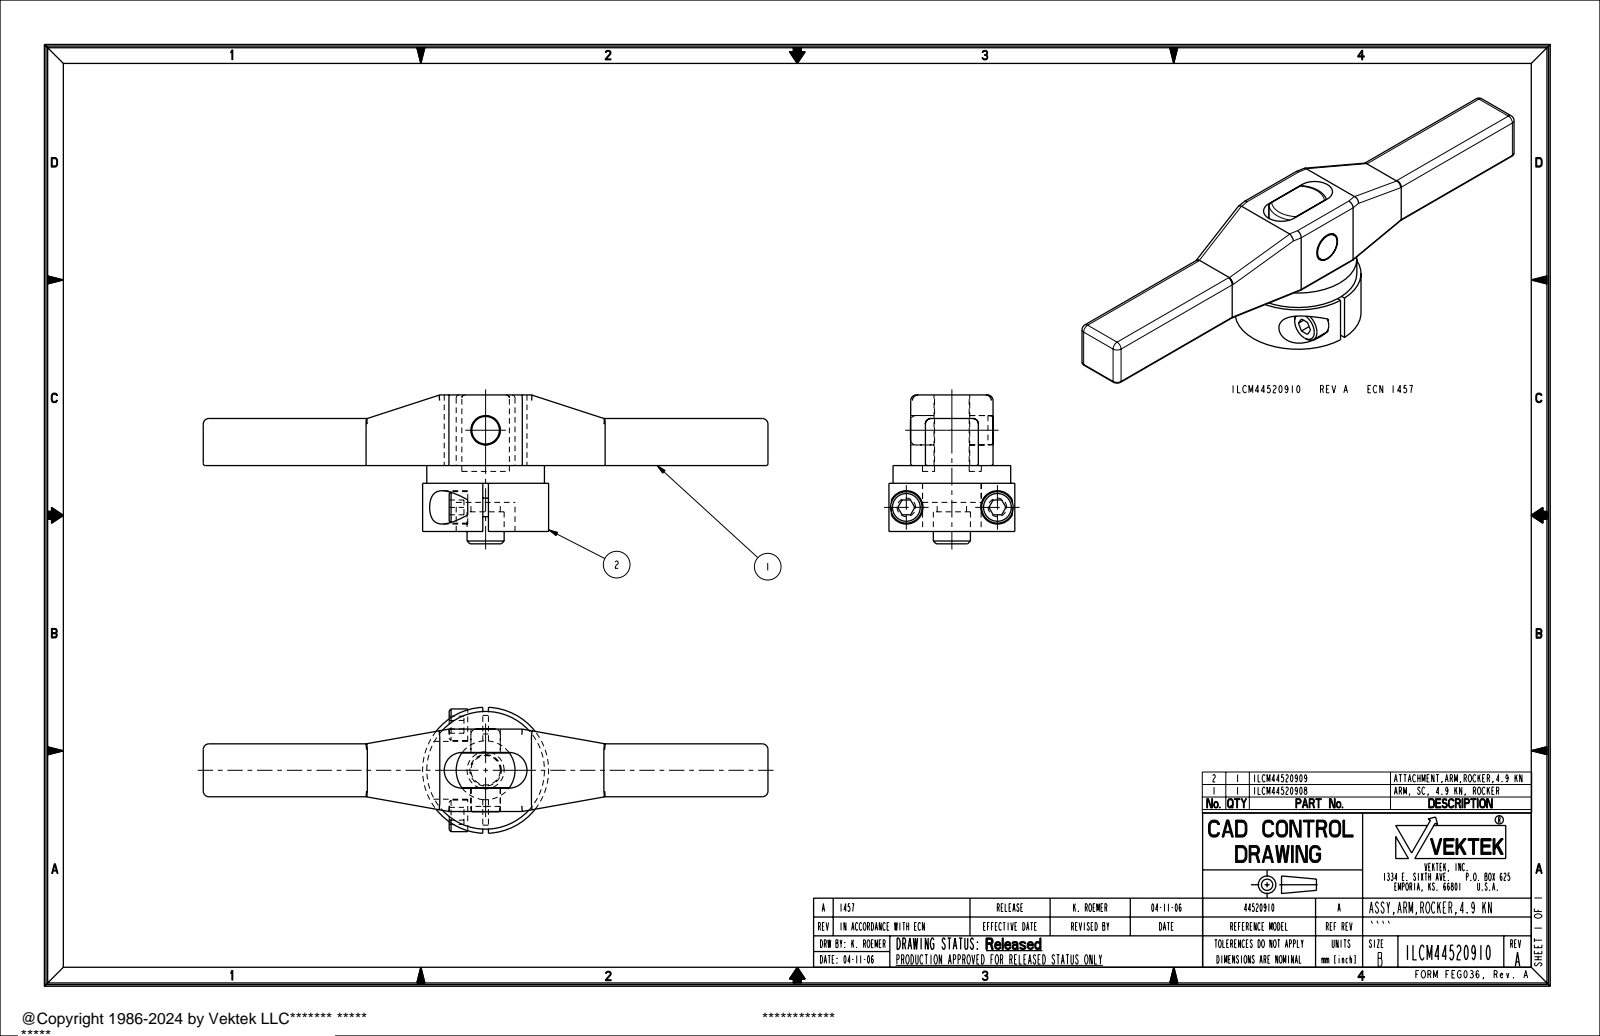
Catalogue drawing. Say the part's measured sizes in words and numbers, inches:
The part is named "ILCM44520909; ILCM44520908; ILCM44520910_ASM". Its 3-D file was written by "PRO/ENGINEER BY PARAMETRIC TECHNOLOGY CORPORATION, 2004290 (AUTOMOTIVE_DESIGN_CC2)". It is 2 solids with 153 faces: 61 planar, 72 cylindrical and 20 other. Overall it measures 6 by 1.581 by 1.337 inches. Its volume is 3.084 cubic inches and its surface area 26.42 square inches. Round holes: 2 of diameter 0.354, 1 of diameter 0.311, 1 of diameter 0.625. Round bosses or shafts: 2 of diameter 0.335, 2 of diameter 0.197, 1 of diameter 1.339, 1 of diameter 1.25, 1 of diameter 0.394, 1 of diameter 0.313, 1 of diameter 0.312. Partial cylindrical surfaces (rounded edges, fillets, slot ends): 22 of radius 0.06, 10 of radius 0.02, 2 of radius 0.189. The main face-to-face distances are 0.562, 0.5, 0.7, 1.2, 0.998, 0.156, 0.719, 0.254, 0.621, 0.097. The hole center spacings are 0.968.
